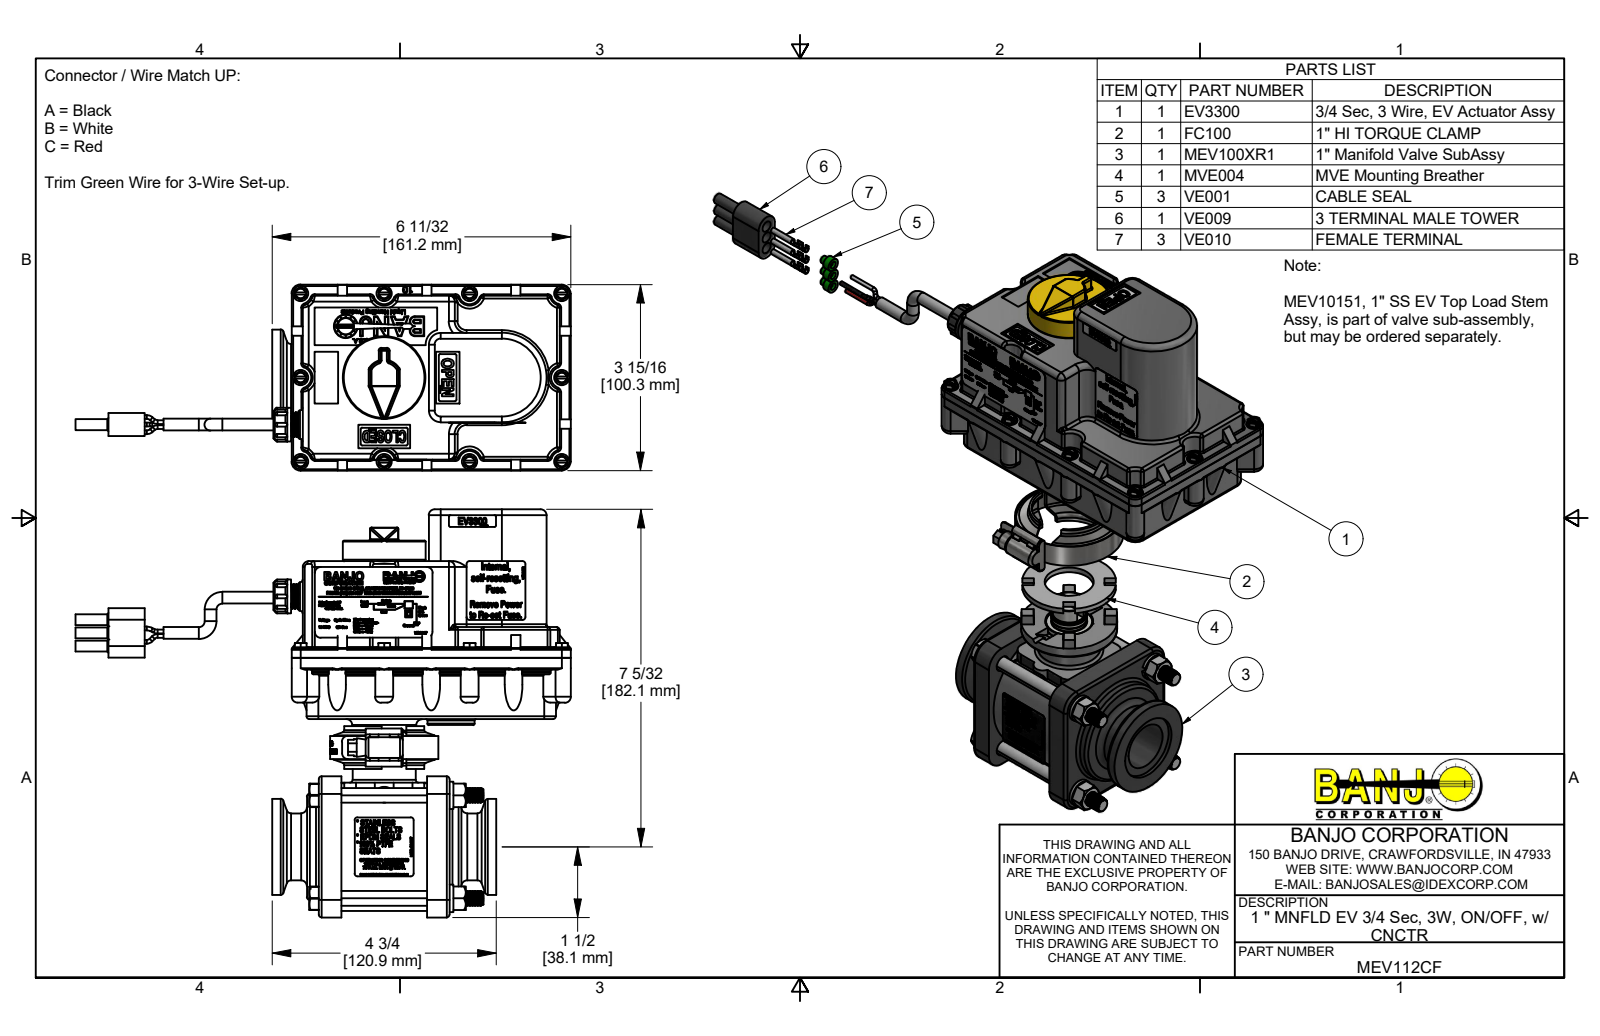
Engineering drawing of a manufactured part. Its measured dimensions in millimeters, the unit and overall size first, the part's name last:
Units: millimetres
Overall size (bounding box): 267.3 × 220.2 × 100.3
Round holes (diameter × count): ⌀2.8 ×10, ⌀4.1 ×10, ⌀5.1 ×10, ⌀1.3 ×8, ⌀2 ×8, ⌀1.2 ×6, ⌀3 ×6, ⌀3.8 ×6, ⌀4.5 ×6, ⌀0.4 ×4, ⌀6.4 ×4, ⌀8.2 ×4
Round bosses / shafts (diameter × count): ⌀6.8 ×60, ⌀8.3 ×10, ⌀3.5 ×10, ⌀2 ×9, ⌀2.6 ×8, ⌀6.4 ×7, ⌀1.9 ×5, ⌀14.8 ×4
Partial cylindrical surfaces — rounded edges, fillets, slot ends (radius × count): R0.8 ×132, R1.5 ×67, R0.5 ×62, R0.9 ×43, R3.2 ×32, R8 ×24, R12.7 ×24, R1.6 ×21
Main face-to-face distances: 3.2, 3.2, 58.4, 27.9, 5.1, 20.1, 19.8, 65.2, 33, 82
Hole centre spacings: 42.7, 52.3, 42.8, 45.3, 60.4, 2.8, 12.5, 30.2
Volume: 917 300 mm³ · Surface area: 404 100 mm²
Bodies: 79 solids, 14177 faces (7111 planar, 1764 cylindrical, 5302 other)
Part name (STEP PRODUCT): MEV112CF; MEV100XR1; MEV10254A; MEV10254AX (+8 more)
STEP written by: Autodesk Inventor 2019 (AUTOMOTIVE_DESIGN)
